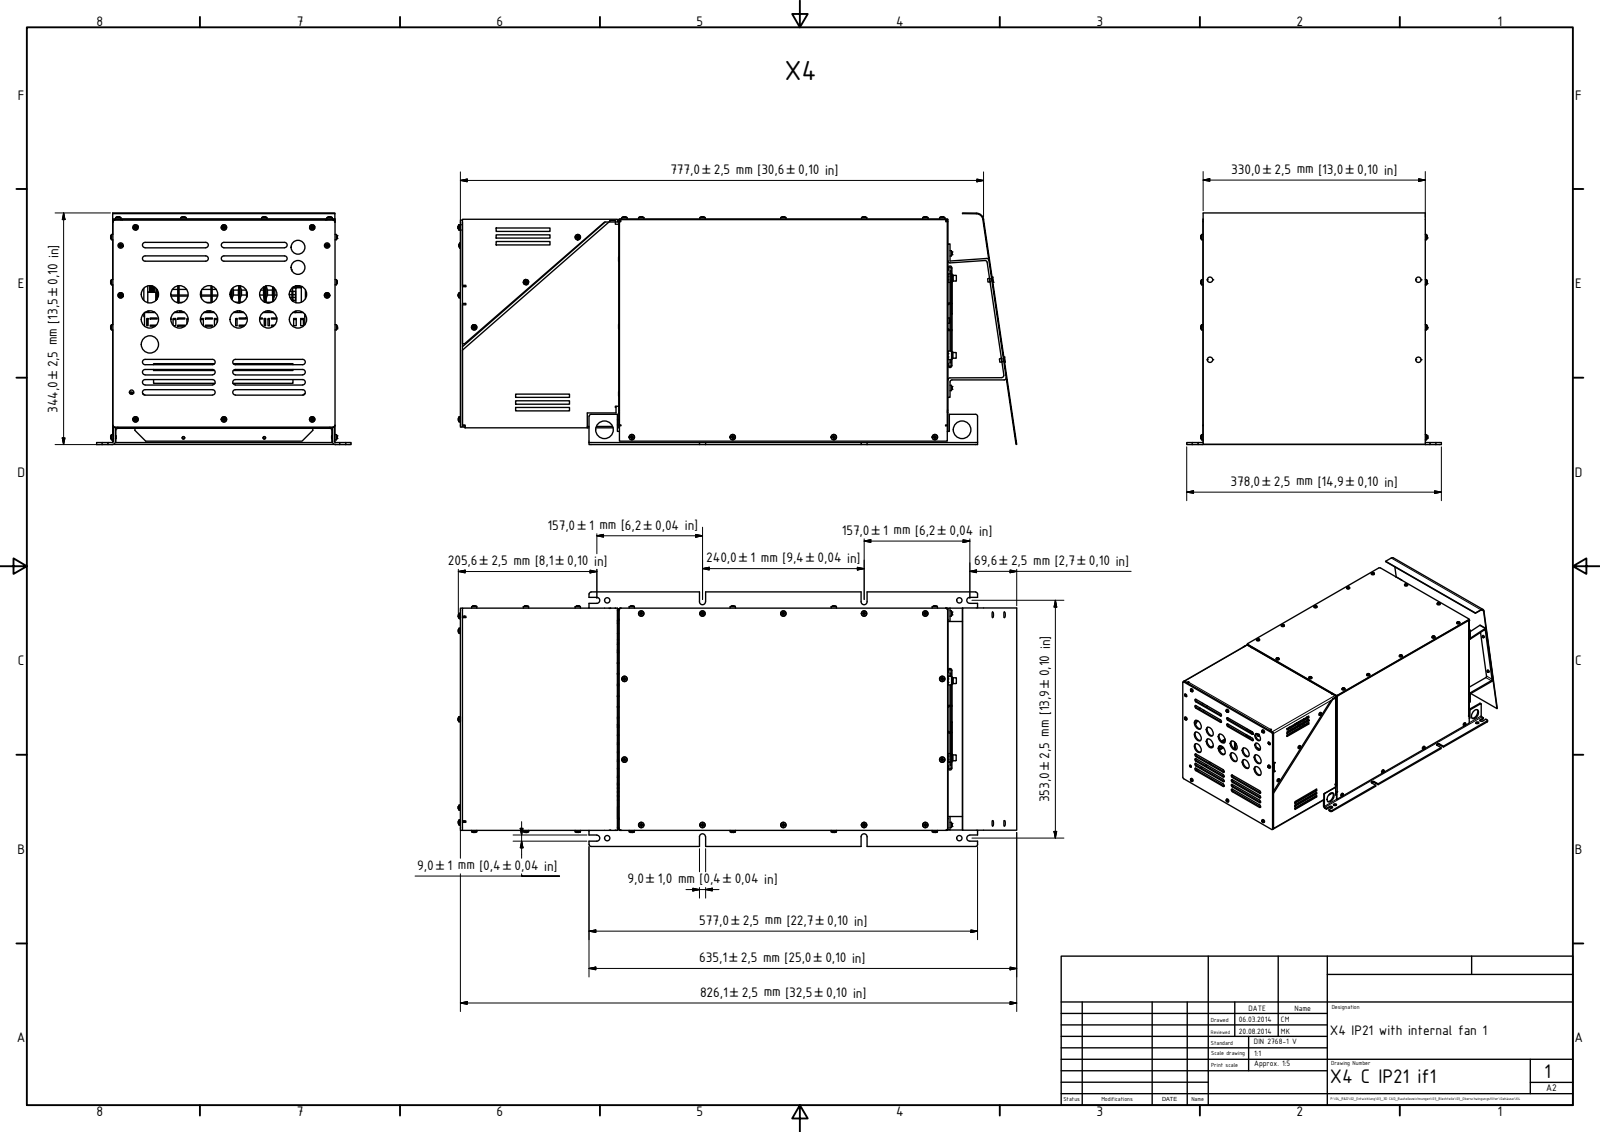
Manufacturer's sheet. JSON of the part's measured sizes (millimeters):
{"part_name": "10100257 Bodenblech X4; 10100395 Seitenwand RHF-BG X4-A; 10100394 Lüfterblech RHF-BG X4-A; 10100393 Deckel RHF-BG X4-A (+8 more)", "step_written_by": "Autodesk Inventor 2015 (AUTOMOTIVE_DESIGN)", "units": "millimeters", "bodies": {"solids": 140, "faces": 9965, "planar": 5948, "cylindrical": 2804, "other": 1213}, "overall_size": [829.46, 378, 343.93], "volume_mm3": 2938000, "surface_area_mm2": 3402000, "round_holes": [[3.24, 46], [5, 38], [6.8, 19], [4, 13], [25.5, 13], [8.25, 12], [8, 10], [7, 6], [11, 6], [6, 5], [6.5, 5], [4.25, 4]], "round_bosses_or_shafts": [[4, 48], [3.65, 41], [1.4, 8], [8, 6], [8.5, 5], [16, 4], [11.4, 4], [9.2, 4]], "partial_cylinders_radius": [[0.5, 109], [0.72, 104], [0.1, 61], [1, 60], [0.15, 58], [2, 51], [0.1, 41], [3, 39]], "face_to_face_distances": [1, 2, 329, 328, 3, 330, 308, 310, 307, 488], "hole_center_spacings": [120, 21, 309.5, 314, 36.37, 27, 46, 23]}
